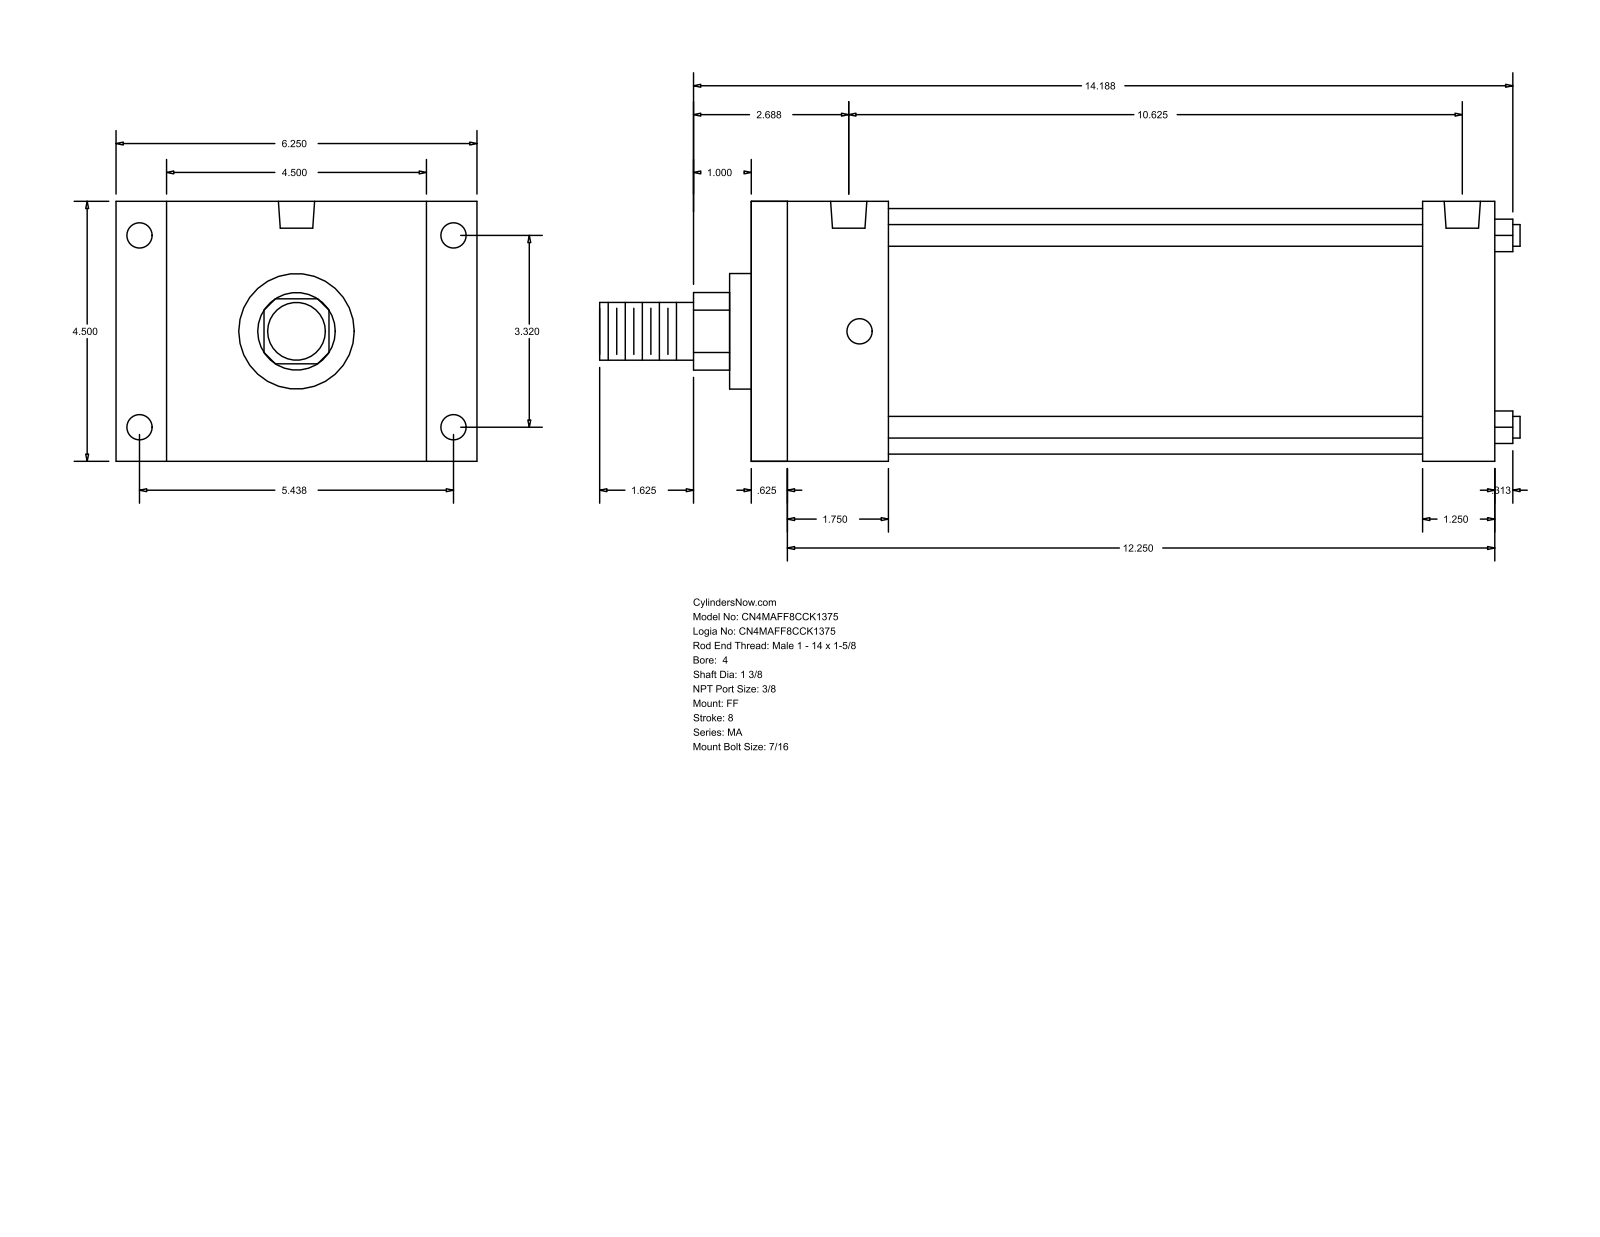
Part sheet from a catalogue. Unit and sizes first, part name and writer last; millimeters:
Units: millimetres
Overall size (bounding box): 404.81 × 158.75 × 114.3
Round holes (diameter × count): ⌀11.11 ×8, ⌀15.93 ×2
Round bosses / shafts (diameter × count): ⌀9.53 ×4, ⌀107.95 ×1, ⌀50.8 ×1, ⌀34.92 ×1, ⌀25.4 ×1
Partial cylindrical surfaces — rounded edges, fillets, slot ends (radius × count): R17.06 ×1
Main face-to-face distances: 114.3, 327.03, 15.87, 311.16, 22.23, 136.53, 295.28, 279.41, 31.75, 60.32
Hole centre spacings: 84.32, 138.12, 161.82, 260.35, 4.76, 4.77, 265.11, 265.12
Bodies: 0 solids, 92 faces (64 planar, 28 cylindrical, 0 other)
Part name (STEP PRODUCT): MA_FF__0400_1.375
STEP written by: GSSL Pune (CONFIG_CONTROL_DESIGN)
